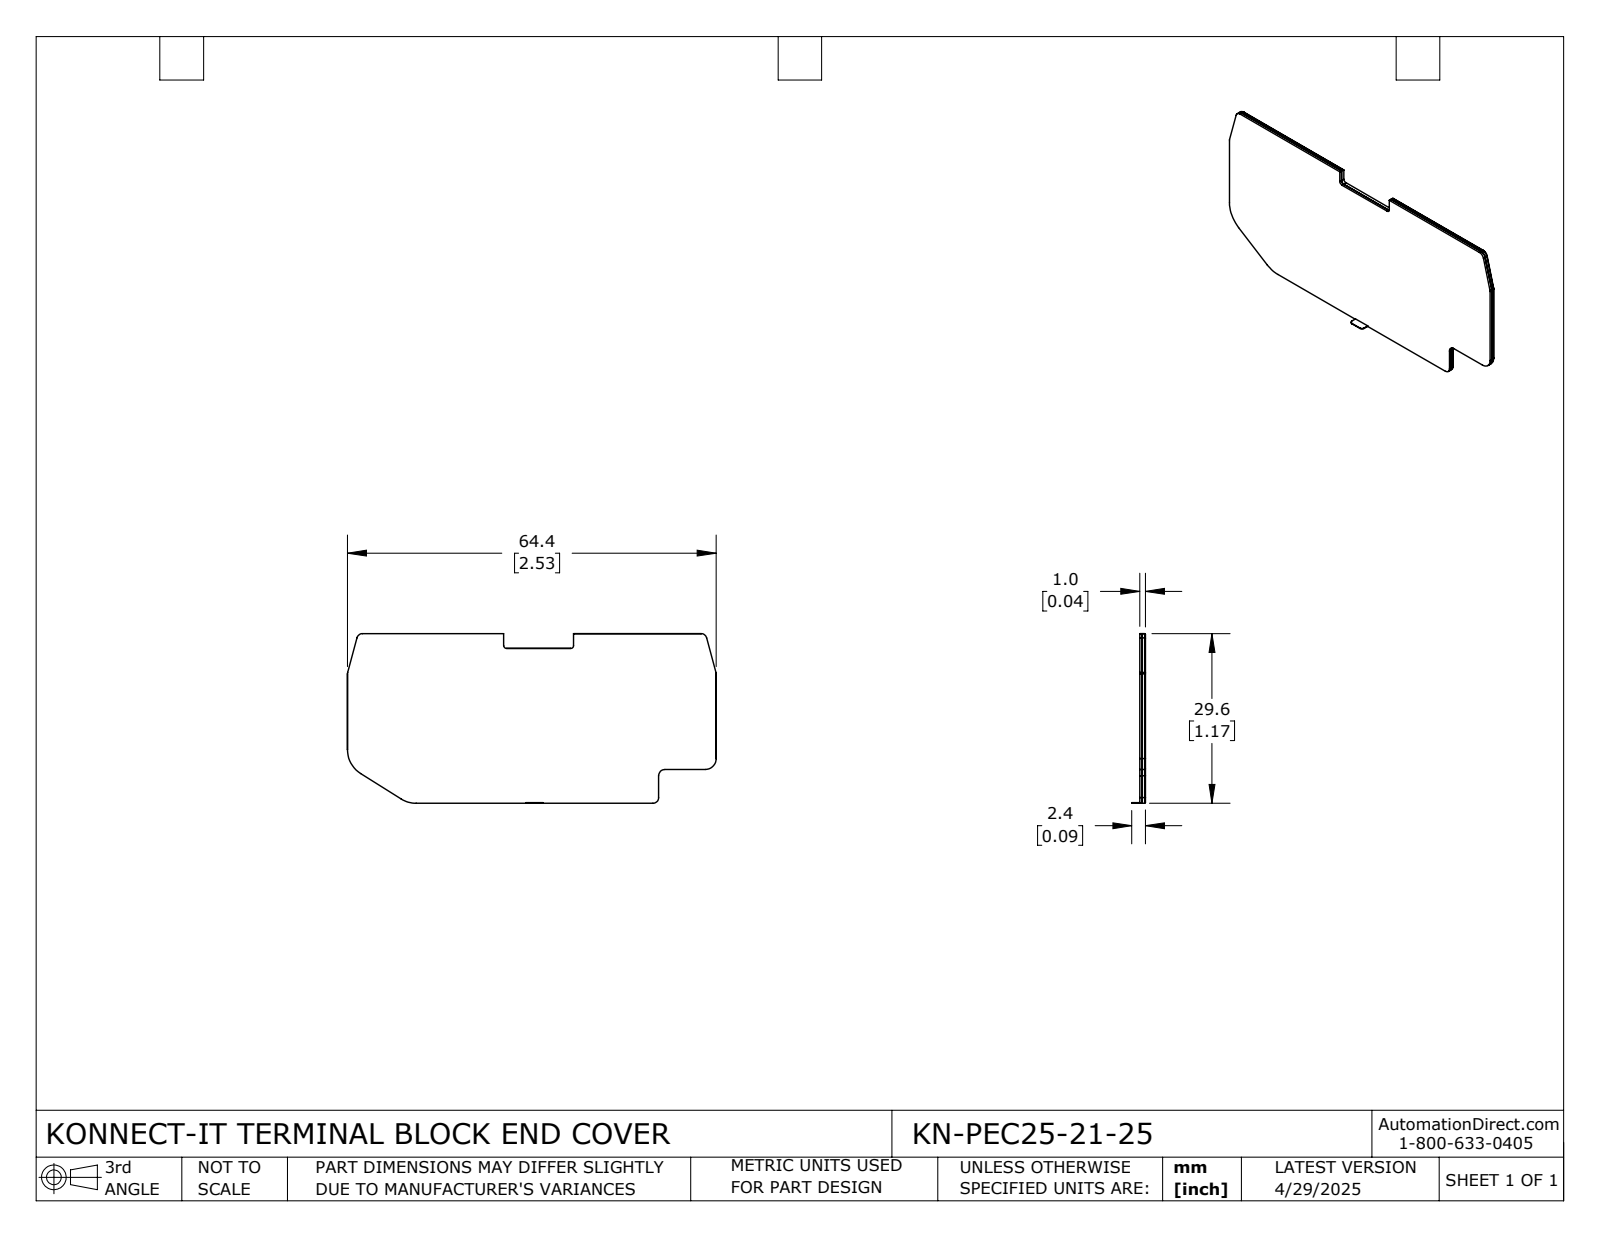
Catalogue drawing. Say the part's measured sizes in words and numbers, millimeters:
The part is named "KN-PEC25-21-25". Its 3-D file was written by "SolidWorks 2024 (CONFIG_CONTROL_DESIGN)". It is 2 solids with 78 faces: 45 planar, 33 cylindrical and 0 other. Overall it measures 64.37 by 29.61 by 2.4 millimeters. Its volume is 1 763 cubic millimeters and its surface area 7 252 square millimeters. Partial cylindrical surfaces (rounded edges, fillets, slot ends): 5 of radius 0.9, 5 of radius 1, 4 of radius 0.5, 2 of radius 4.8, 2 of radius 4.9, 1 of radius 1.1, 1 of radius 1.2, 1 of radius 1.8. The main face-to-face distances are 0.42, 1, 0.58, 29.61, 29.51, 0.85, 0.43, 64.37, 27.02, 2.59.
